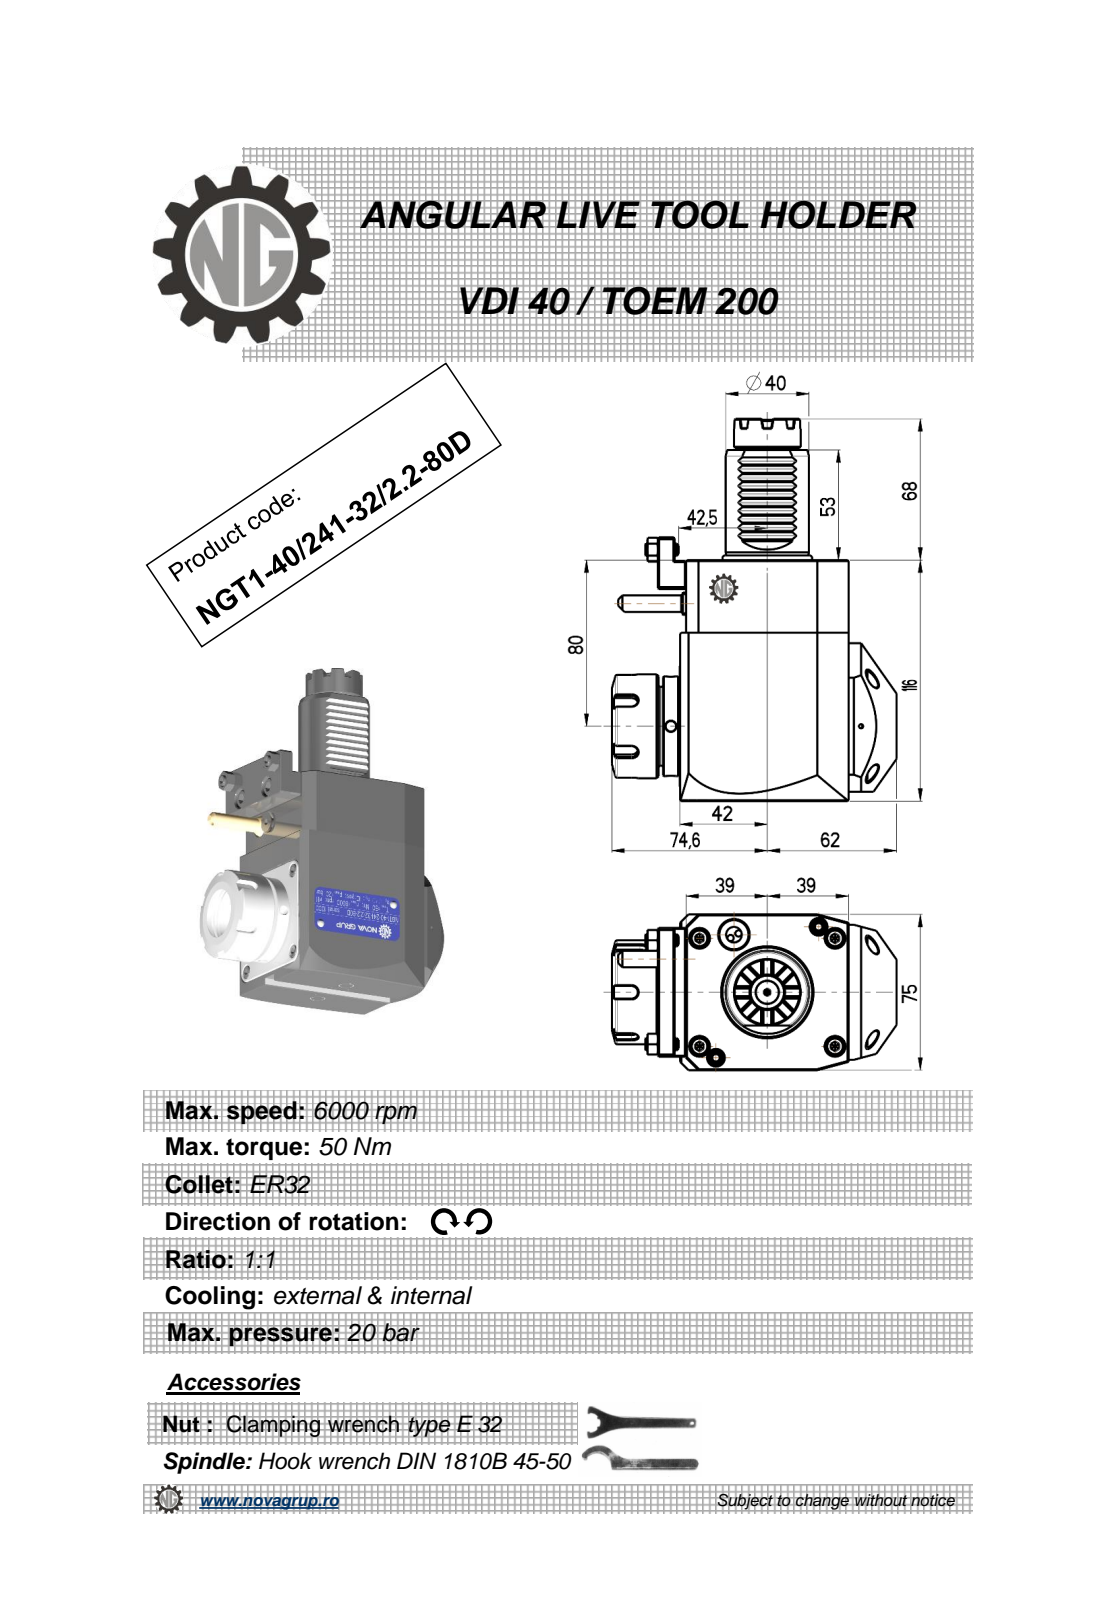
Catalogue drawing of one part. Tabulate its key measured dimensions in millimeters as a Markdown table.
| quantity | value |
| --- | --- |
| part name | NGT1_40_241_32_2_2_80D |
| STEP written by | PRO/ENGINEER BY PARAMETRIC TECHNOLOGY CORPORATION, 2010280 (CONFIG_CONTROL_DESIGN) |
| units | millimeters |
| bodies | 1 solid, 473 faces (207 planar, 89 cylindrical, 177 other) |
| overall size | 184 × 136.6 × 76.6 |
| volume | 897 905 mm³ |
| surface area | 72 438 mm² |
| round holes (diameter × count) | 5 × 3, 3 × 1, 27 × 1 |
| round bosses / shafts (diameter × count) | 6 × 2, 50 × 1, 48 × 1, 41 × 1, 40 × 1, 32 × 1, 17 × 1, 11.2 × 1 |
| partial cylindrical surfaces (radius × count) | 0.3 × 10, 0.31 × 10, 0.22 × 6, 3 × 5, 0.5 × 1, 8.6 × 1, 40 × 1 |
| main face-to-face distances | 75, 116, 81, 13.5, 80.8, 0.5, 10.5, 10.7, 91.5, 112 |
| hole center spacings | 61.13 |
